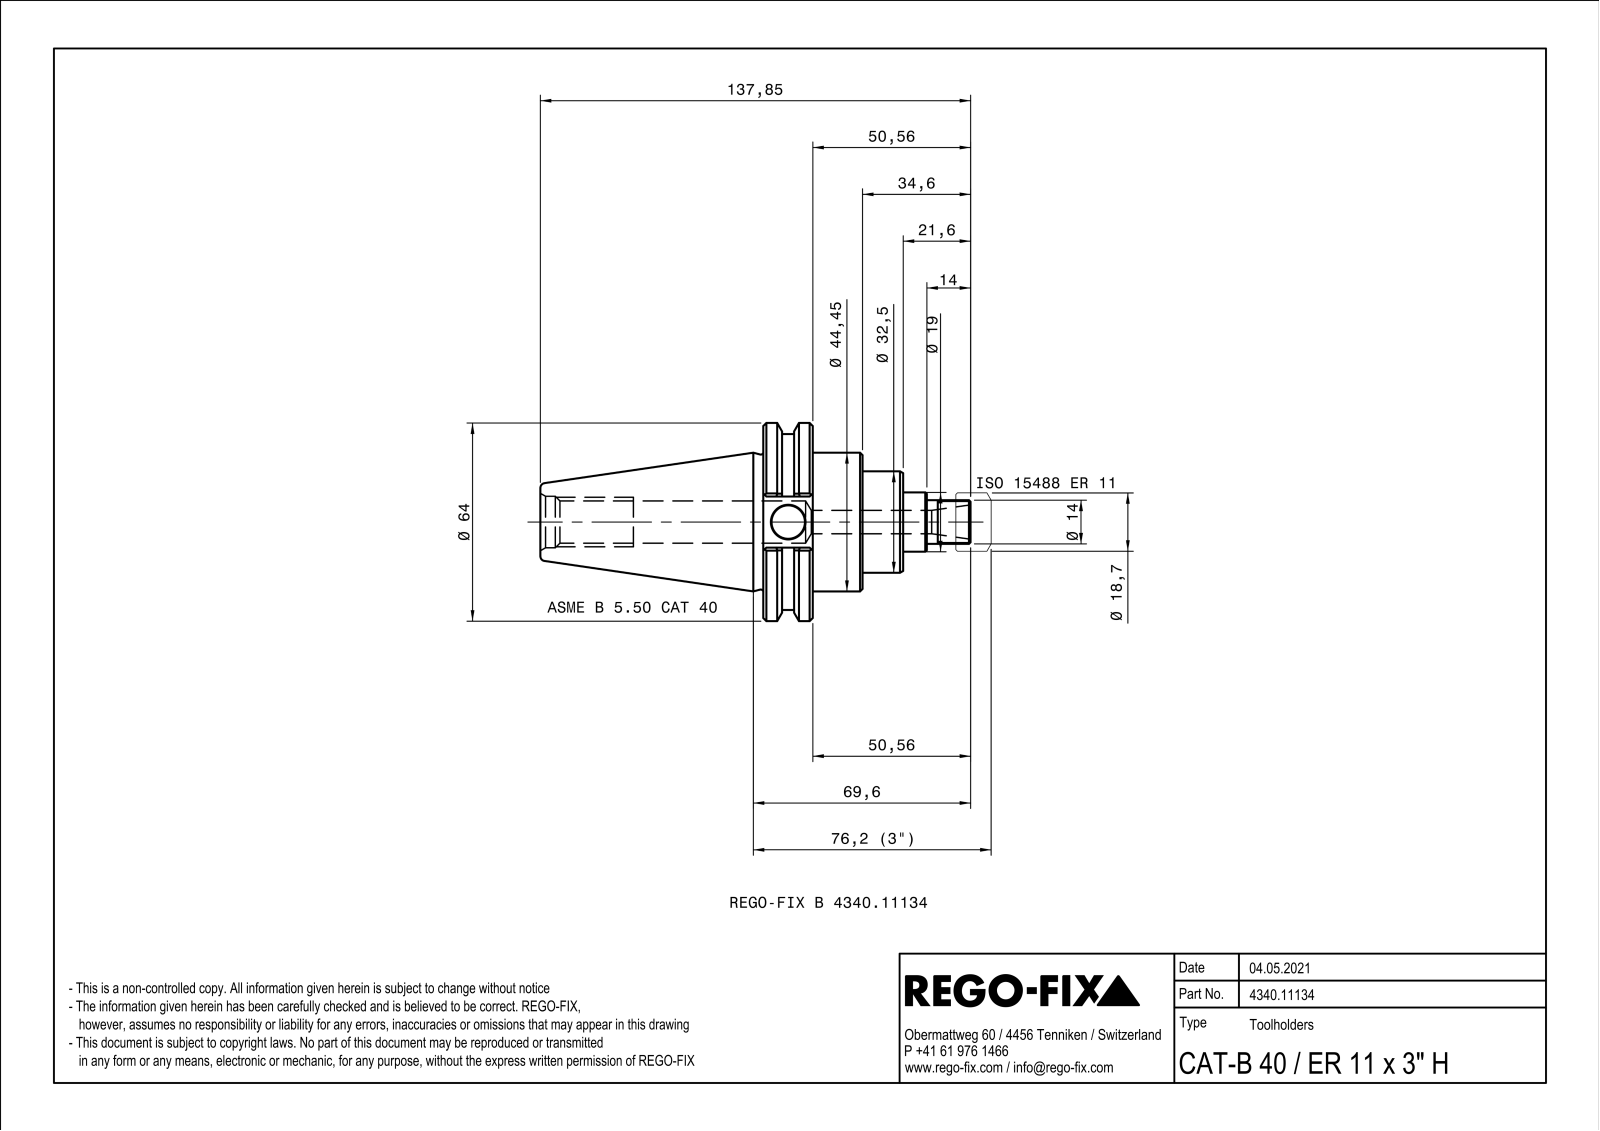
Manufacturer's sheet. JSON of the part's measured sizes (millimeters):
{"part_name": "NOCUT", "step_written_by": "SIEMENS PLM Software Solid Edge ST10 (AUTOMOTIVE_DESIGN)", "units": "millimeters", "bodies": {"solids": 1, "faces": 131, "planar": 37, "cylindrical": 37, "other": 57}, "overall_size": [137.85, 63.5, 60.79], "volume_mm3": 136246, "surface_area_mm2": 26699, "round_holes": [[3.9, 3], [7.5, 1], [10.7, 1], [13.53, 1], [16.5, 1]], "round_bosses_or_shafts": [[63.5, 1], [44.45, 1], [32.5, 1], [19, 1], [14, 1]], "partial_cylinders_radius": [[0.5, 4], [2.25, 2], [28.18, 1]], "face_to_face_distances": [15.87, 15.96, 31.83, 13, 28.96, 44.83, 47.33, 16.38, 116.25, 103.25]}
